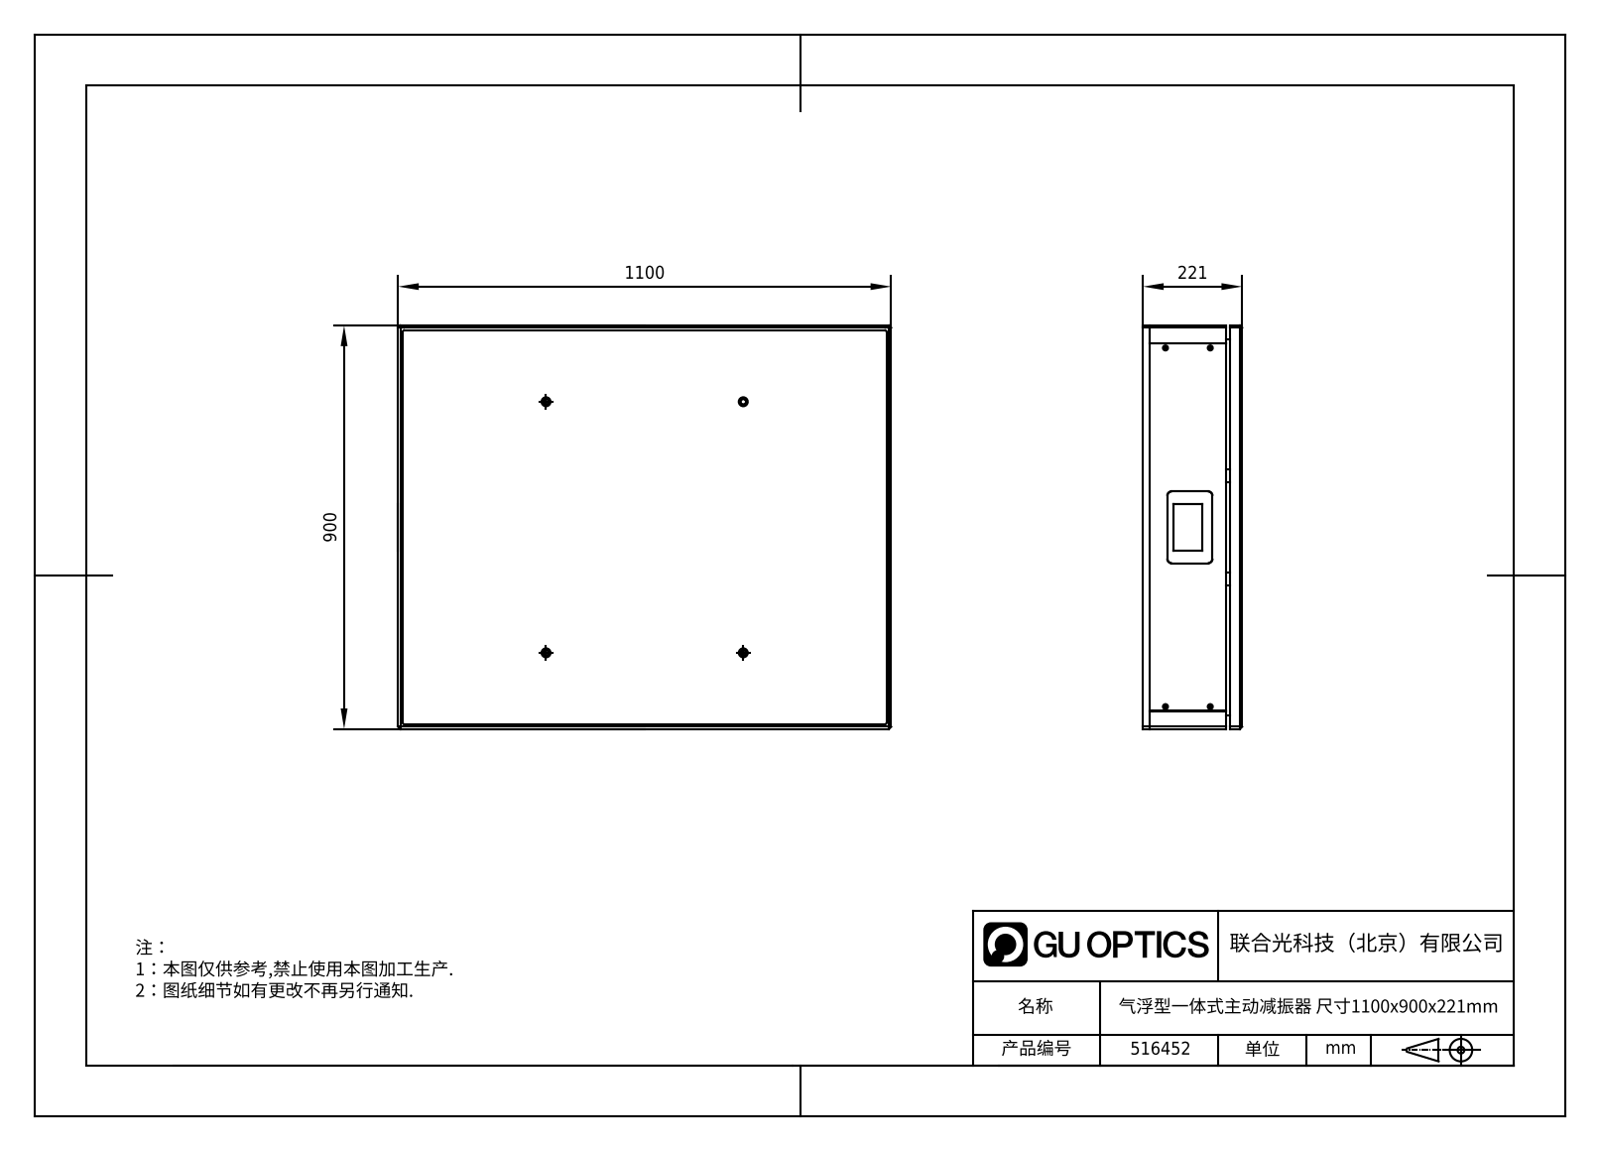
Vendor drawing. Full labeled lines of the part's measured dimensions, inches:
Part name (STEP PRODUCT): 516452
STEP written by: SolidWorks 2020 (CONFIG_CONTROL_DESIGN)
Units: inches
Bodies: 0 solids, 1474 faces (773 planar, 556 cylindrical, 145 other)
Overall size (bounding box): 43.358 × 35.433 × 8.701
Round holes (diameter × count): ⌀0.165 ×42, ⌀0.098 ×27, ⌀0.335 ×19, ⌀0.402 ×16, ⌀0.866 ×16, ⌀0.13 ×14, ⌀0.197 ×14, ⌀0.138 ×8, ⌀0.217 ×8, ⌀0.26 ×8, ⌀0.433 ×8, ⌀0.177 ×5
Round bosses / shafts (diameter × count): ⌀0.039 ×9, ⌀0.315 ×6, ⌀0.276 ×4, ⌀0.551 ×2, ⌀0.383 ×2, ⌀0.236 ×2, ⌀2.362 ×1, ⌀1.89 ×1
Partial cylindrical surfaces — rounded edges, fillets, slot ends (radius × count): R0.197 ×40, R0.118 ×34, R0.079 ×22, R0.02 ×12, R0.039 ×8, R0.157 ×8, R0.394 ×8, R0.067 ×5
Main face-to-face distances: 0.945, 8.031, 7.087, 0.591, 7.677, 8.622, 1.024, 0.079, 8.701, 8.11
Hole centre spacings: 1.748, 3.496, 4.488, 5.414, 2.783, 4.134, 2.55, 3.937
